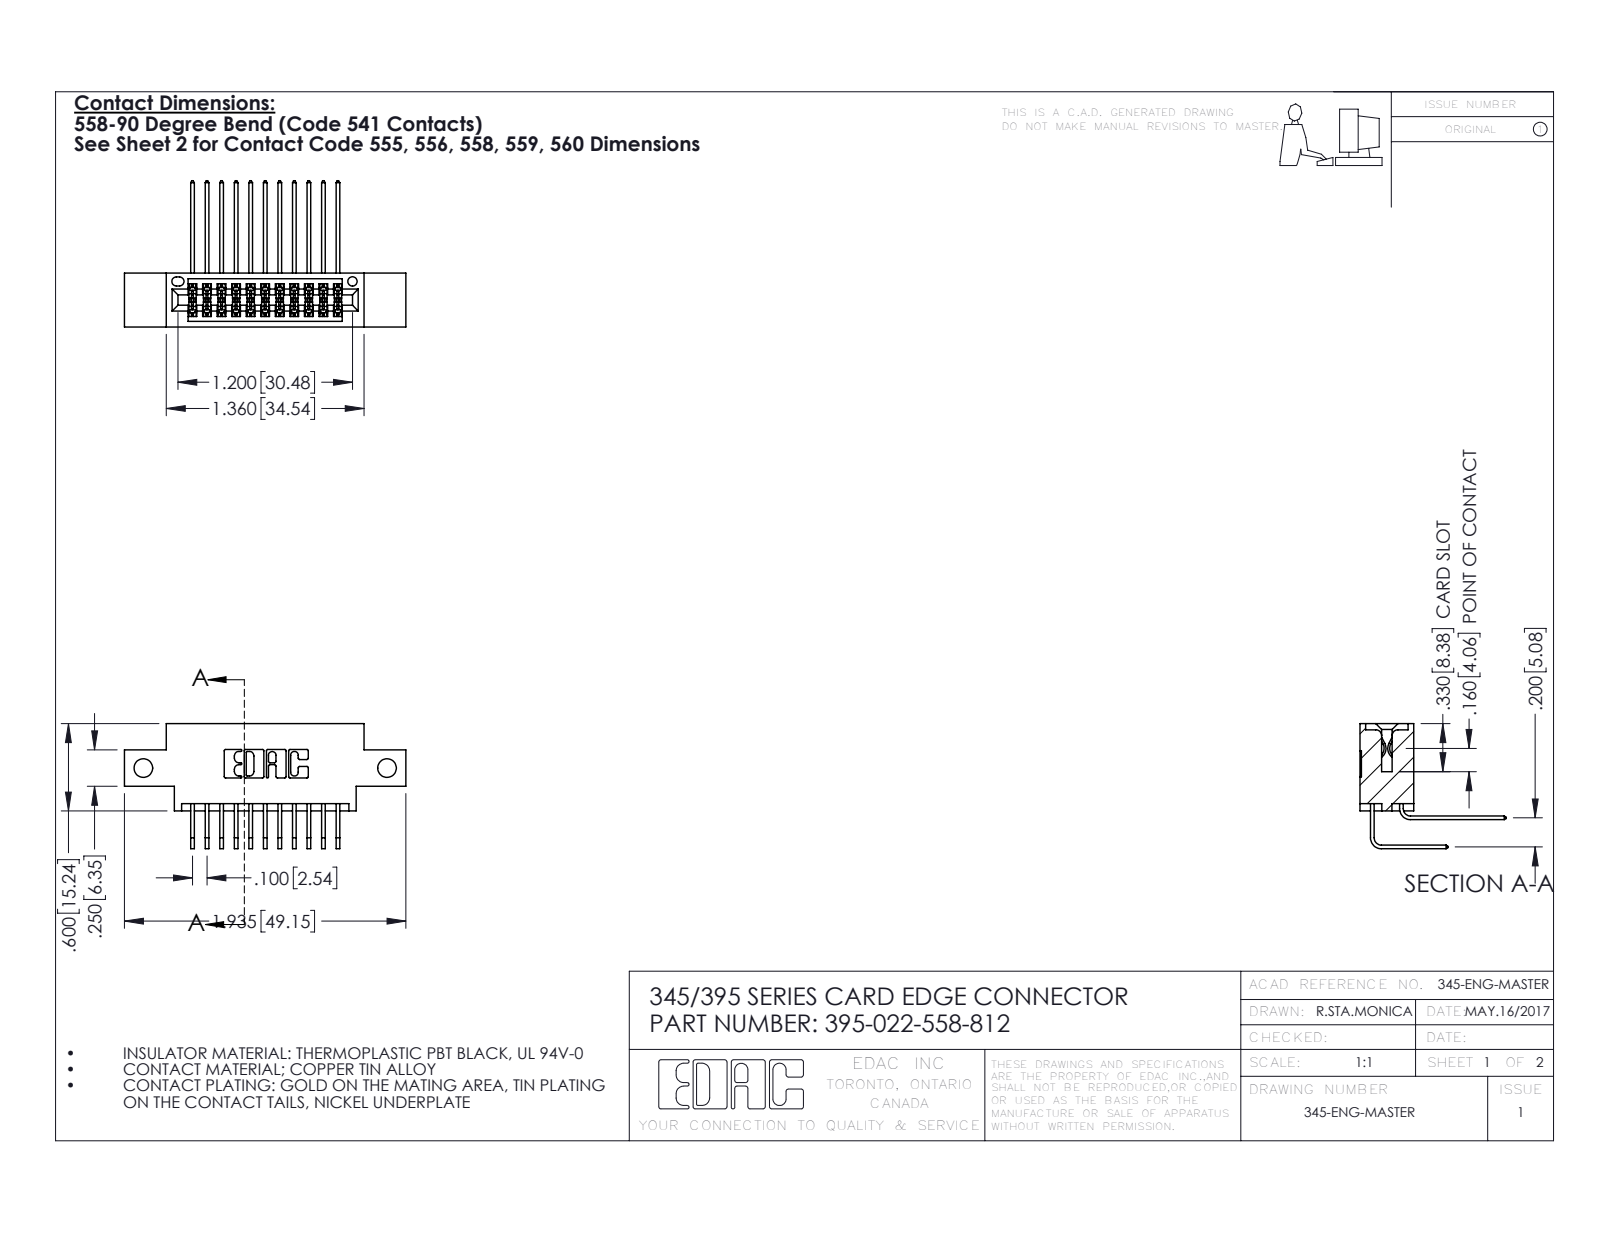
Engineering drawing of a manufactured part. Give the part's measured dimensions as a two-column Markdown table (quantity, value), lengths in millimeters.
| quantity | value |
| --- | --- |
| part name | 345-292-001_558 559 Tail - 1; 395-022-558-812; 345-292-001_558 Tail - 2; 345 Part_0.170 Offset - Side Mount |
| STEP written by | SolidWorks 2016 (CONFIG_CONTROL_DESIGN) |
| units | millimeters |
| bodies | 23 solids, 1274 faces (854 planar, 420 cylindrical, 0 other) |
| overall size | 49.1 × 25.5 × 21.8 |
| volume | 4 410 mm³ |
| surface area | 6 529 mm² |
| round holes (diameter × count) | 3.3 × 2, 1.6 × 1 |
| partial cylindrical surfaces (radius × count) | 0.2 × 34, 0.3 × 22, 0.2 × 6, 0.8 × 6, 0.7 × 3, 0.4 × 2, 0.5 × 2, 0.6 × 2 |
| main face-to-face distances | 5.1, 1.8, 7.6, 9.4, 2.5, 6.9, 0.6, 2.5, 5.7, 4.4 |
| hole center spacings | 42.5 |
